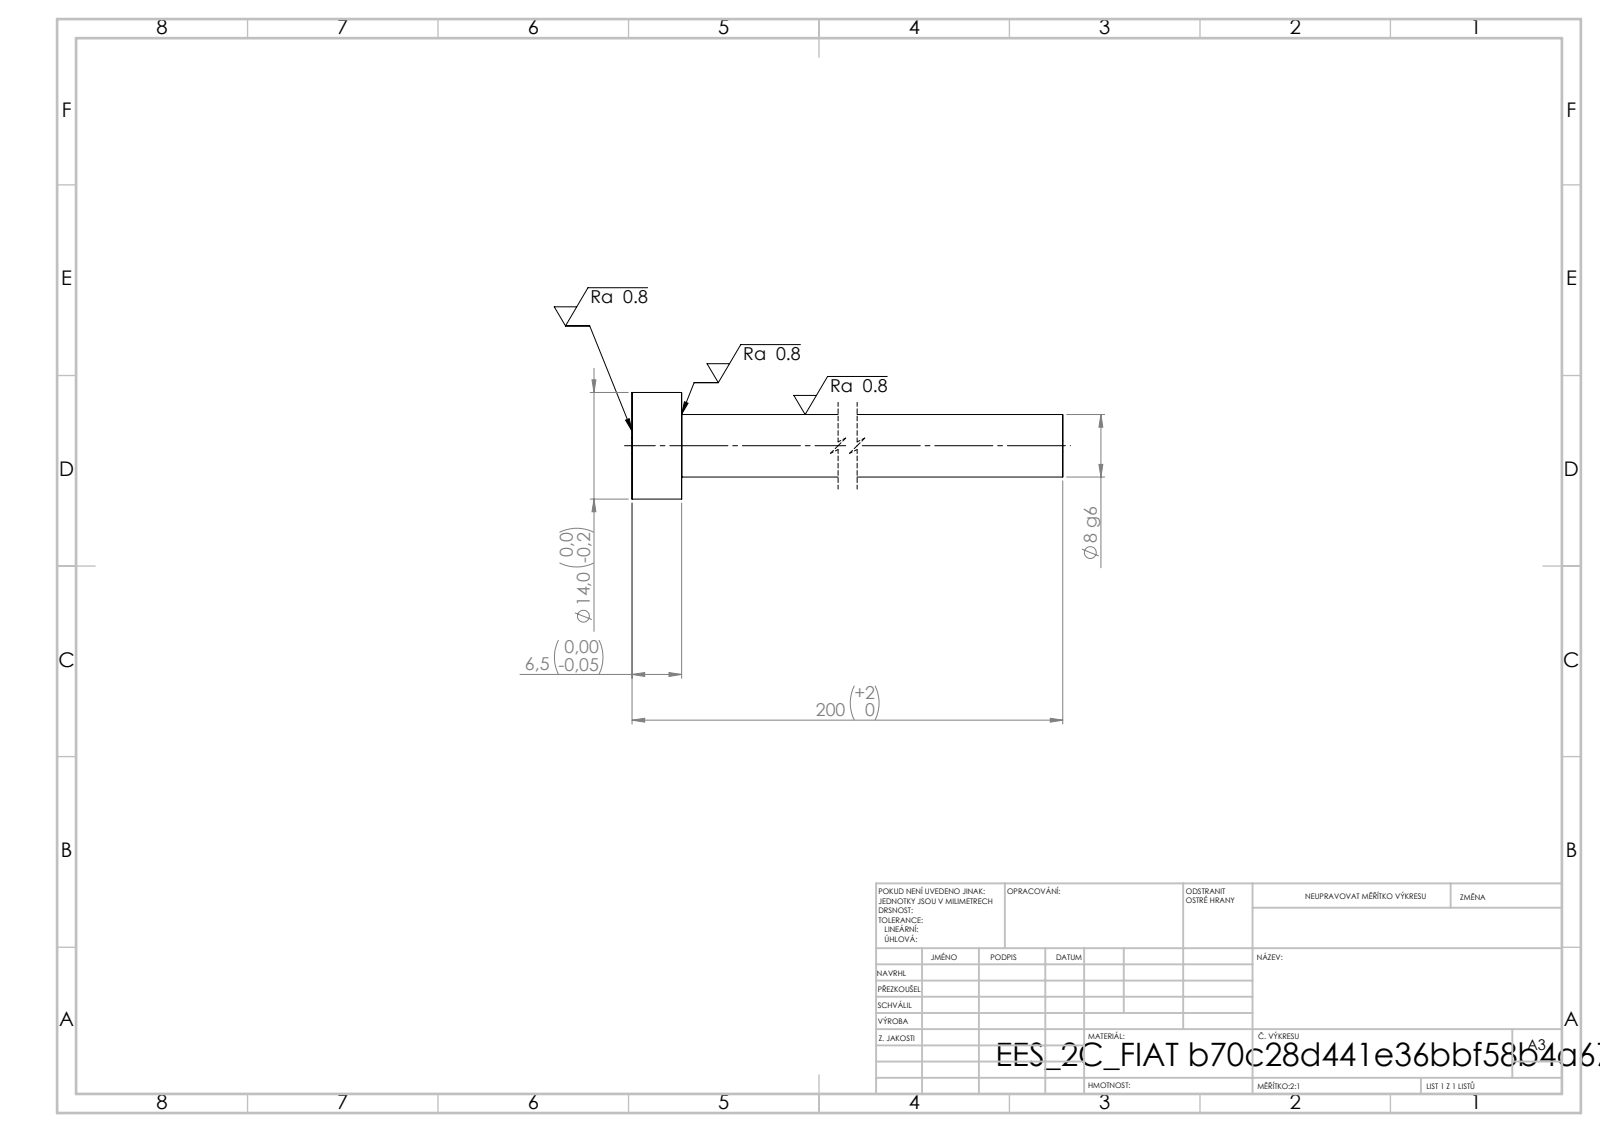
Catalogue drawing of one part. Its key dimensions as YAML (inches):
step_written_by: "SolidWorks 2019 (CONFIG_CONTROL_DESIGN)"
units: inches
bodies: {solids: 1, faces: 7, planar: 3, cylindrical: 4, other: 0}
overall_size: [7.874, 0.551, 0.551]
volume: 0.685
surface_area: 8.647
round_bosses_or_shafts:
  - {diameter: 0.551, count: 1}
  - {diameter: 0.323, count: 1}
face_to_face_distances: [0.256, 7.874, 7.618]
